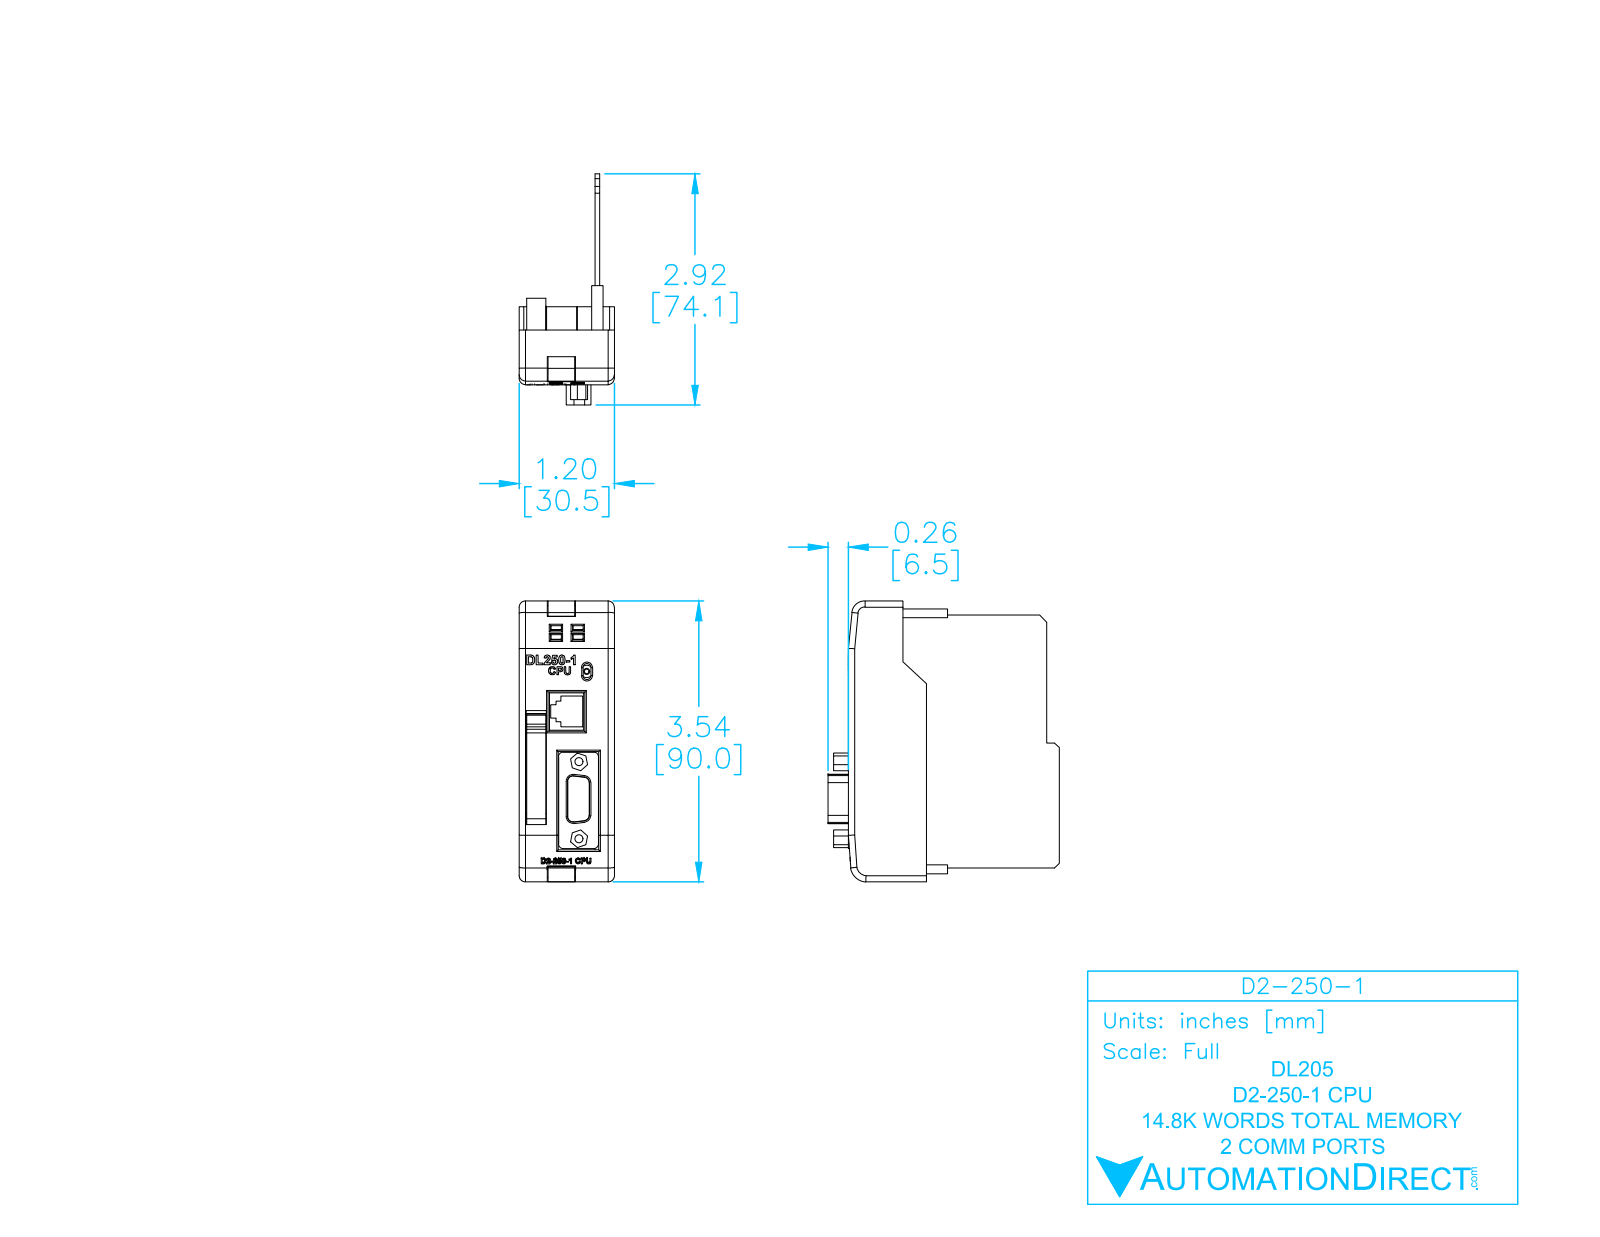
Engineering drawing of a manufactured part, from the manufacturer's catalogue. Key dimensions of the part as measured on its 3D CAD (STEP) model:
Part name (STEP PRODUCT): D2-250-1
STEP written by: SolidWorks 2009 (AUTOMOTIVE_DESIGN)
Units: millimetres
Bodies: 6 solids, 637 faces (375 planar, 108 cylindrical, 154 other)
Overall size (bounding box): 90 × 74.07 × 30.5
Volume: 24 901 mm³ · Surface area: 33 751 mm²
Round holes (diameter × count): ⌀2.5 ×2
Round bosses / shafts (diameter × count): ⌀4 ×1, ⌀2 ×1, ⌀1.5 ×1
Partial cylindrical surfaces — rounded edges, fillets, slot ends (radius × count): R0.5 ×33, R2 ×10, R1.75 ×8, R0.25 ×4, R1.5 ×4, R2.25 ×4, R1.25 ×2, R0.42 ×1
Main face-to-face distances: 1.5, 24.28, 4.72, 29, 25.78, 30.5, 6.22, 22.78, 27.5, 3.22
Hole centre spacings: 24.67
